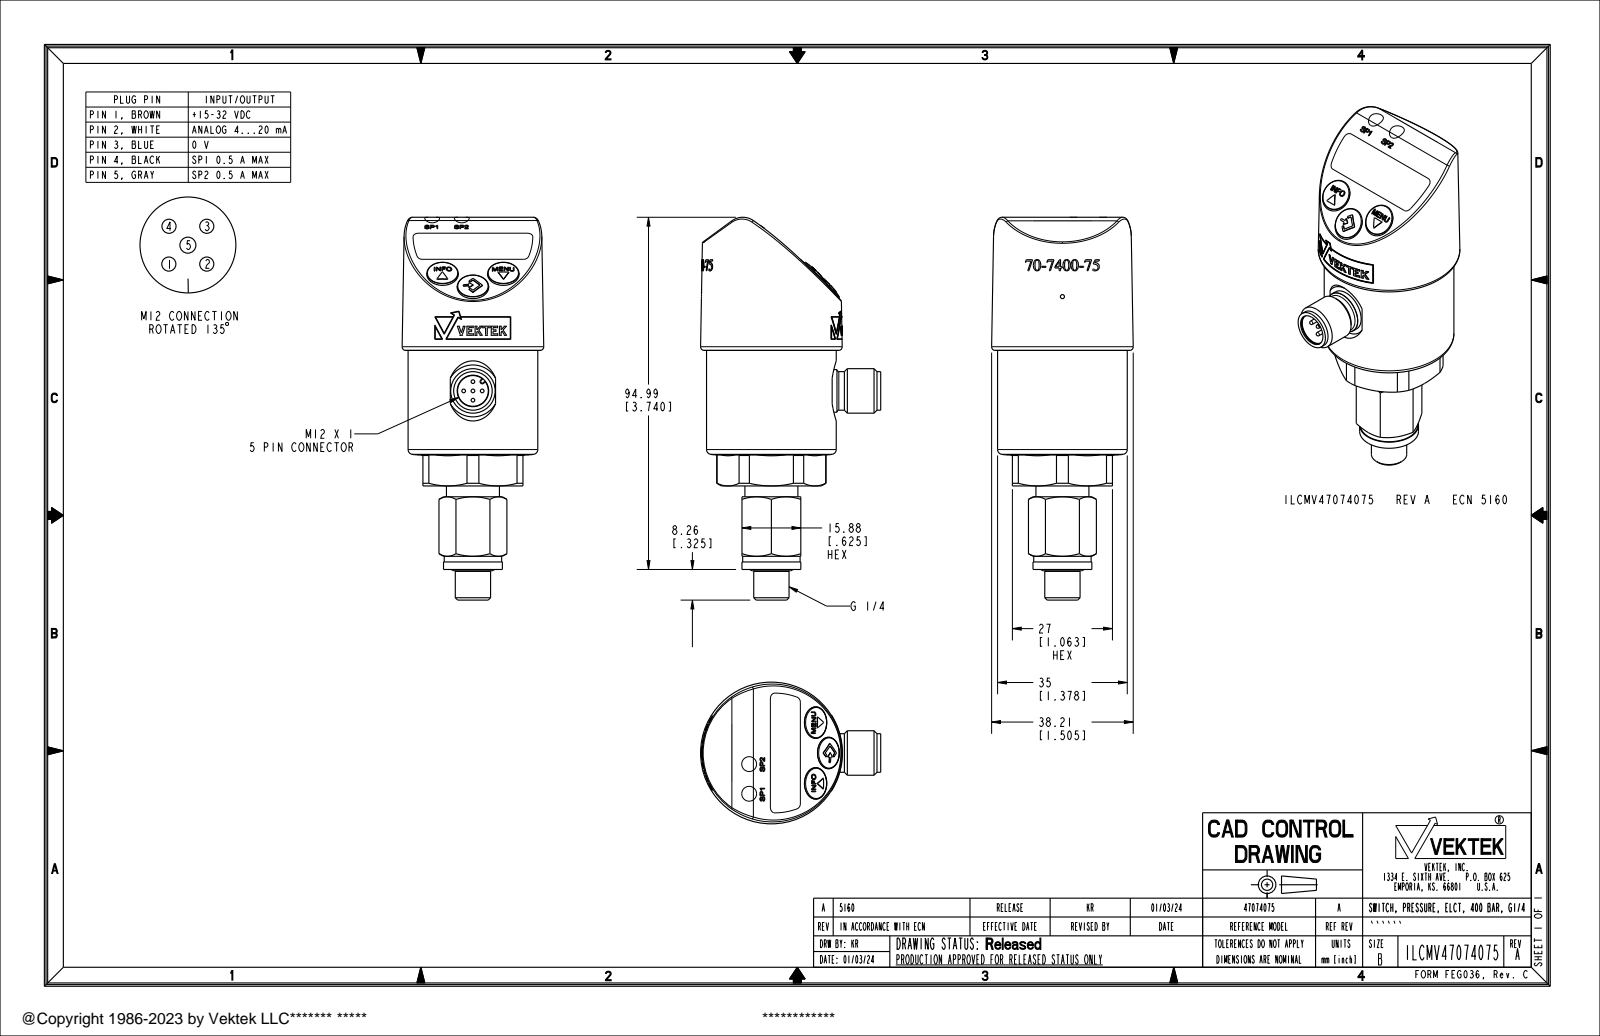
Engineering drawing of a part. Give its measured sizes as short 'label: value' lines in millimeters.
name: ILCMV47074075
written by: CREO PARAMETRIC BY PTC INC, 2021164 (AUTOMOTIVE_DESIGN)
unit: mm
bodies: 9 solids, 828 faces (336 planar, 103 cylindrical, 389 other)
size: 103.25 × 48.61 × 38.22
volume: 69 962 mm³; area: 13 654 mm²
holes: 1× ⌀1.1, 1× ⌀3.5, 1× ⌀4.57, 1× ⌀8.3, 1× ⌀8.5, 1× ⌀9.5, 1× ⌀9.96, 1× ⌀10.37, 1× ⌀11.84, 1× ⌀31.42, 1× ⌀35.4
bosses: 5× ⌀1, 1× ⌀35, 1× ⌀30.2, 1× ⌀15.88, 1× ⌀15.49, 1× ⌀14.3, 1× ⌀12, 1× ⌀11.5
rounds: 6× R0.1, 2× R0.2, 1× R0.6, 1× R5, 1× R11.18, 1× R14.75, 1× R16.4, 1× R19.11
face distances: 15.88, 27, 22.53, 30.93, 8.4, 31.2, 8.67, 10.47, 12.06, 20.46
hole spacings: 25.43
